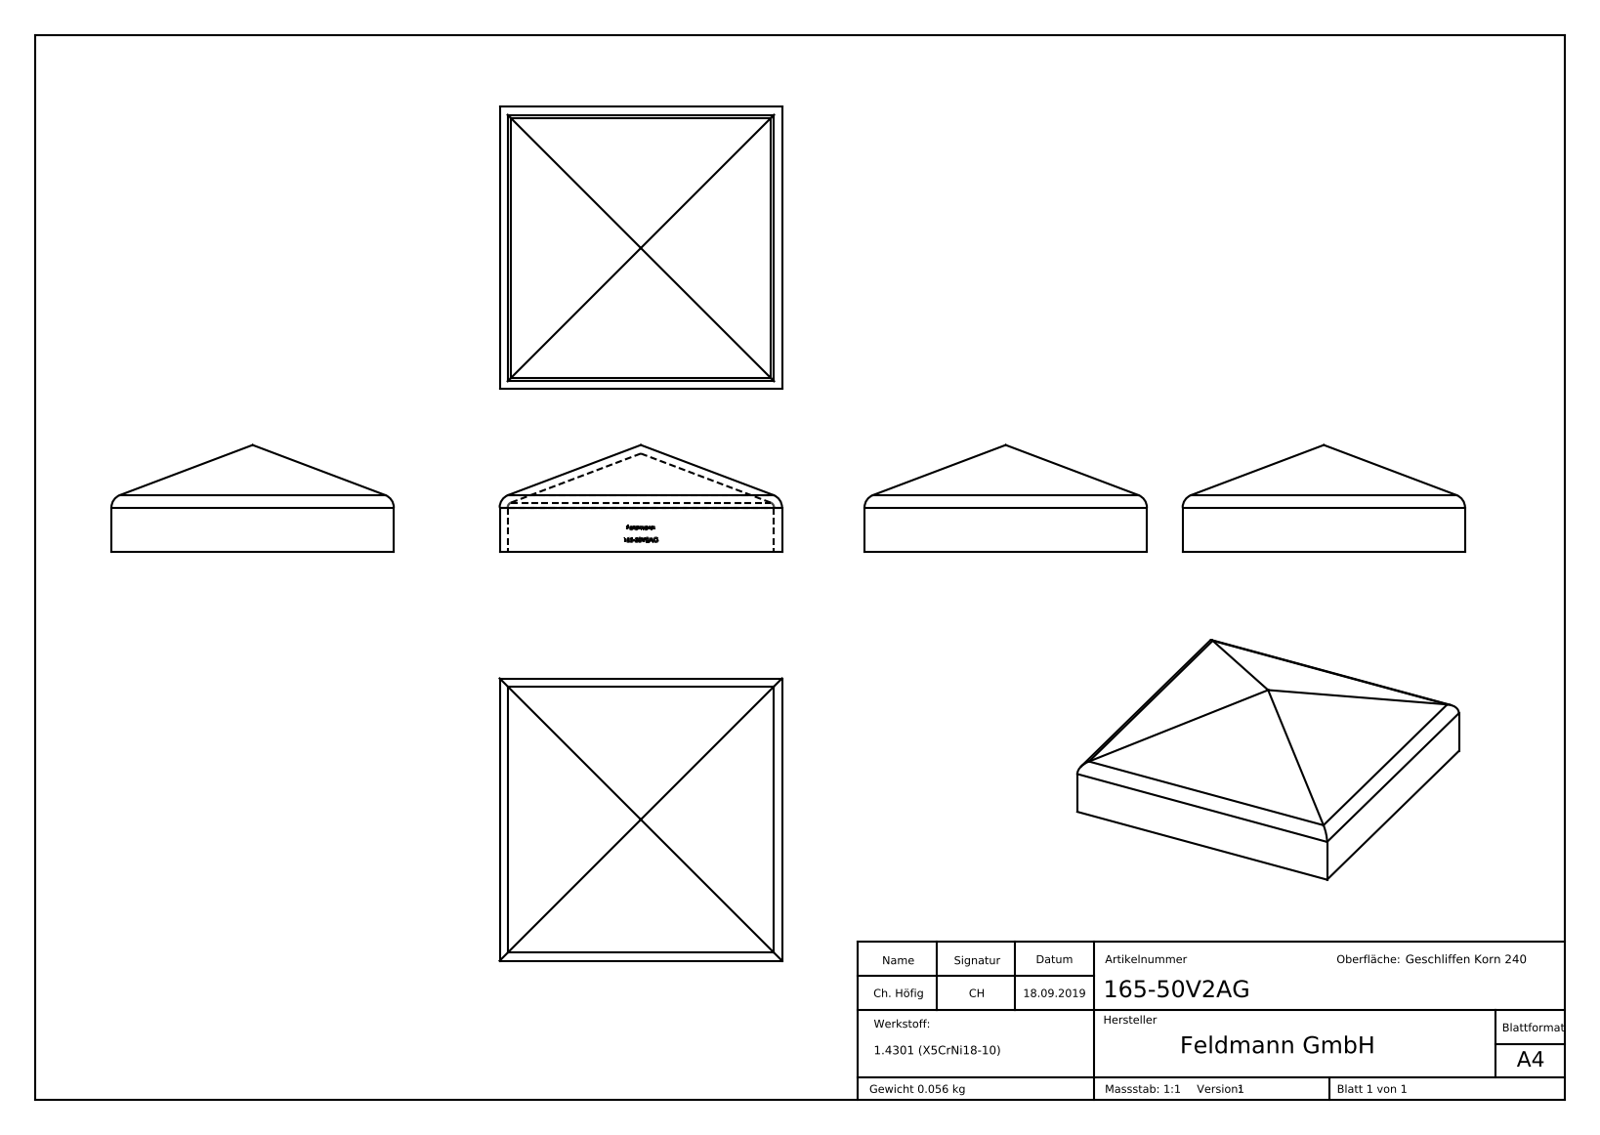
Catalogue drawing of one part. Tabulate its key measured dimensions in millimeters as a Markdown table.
| quantity | value |
| --- | --- |
| part name | 165-50V2AG |
| STEP written by | SolidWorks 2015 (CONFIG_CONTROL_DESIGN) |
| units | millimeters |
| bodies | 1 solid, 257 faces (148 planar, 12 cylindrical, 97 other) |
| overall size | 53 × 53 × 20 |
| volume | 7 089 mm³ |
| surface area | 9 774 mm² |
| partial cylindrical surfaces (radius × count) | 1 × 4, 2.5 × 4, 0.1 × 2 |
| main face-to-face distances | 1.5, 51.5, 1.51, 53, 50, 1.4, 50.1, 51.6, 0.45, 2.61 |
